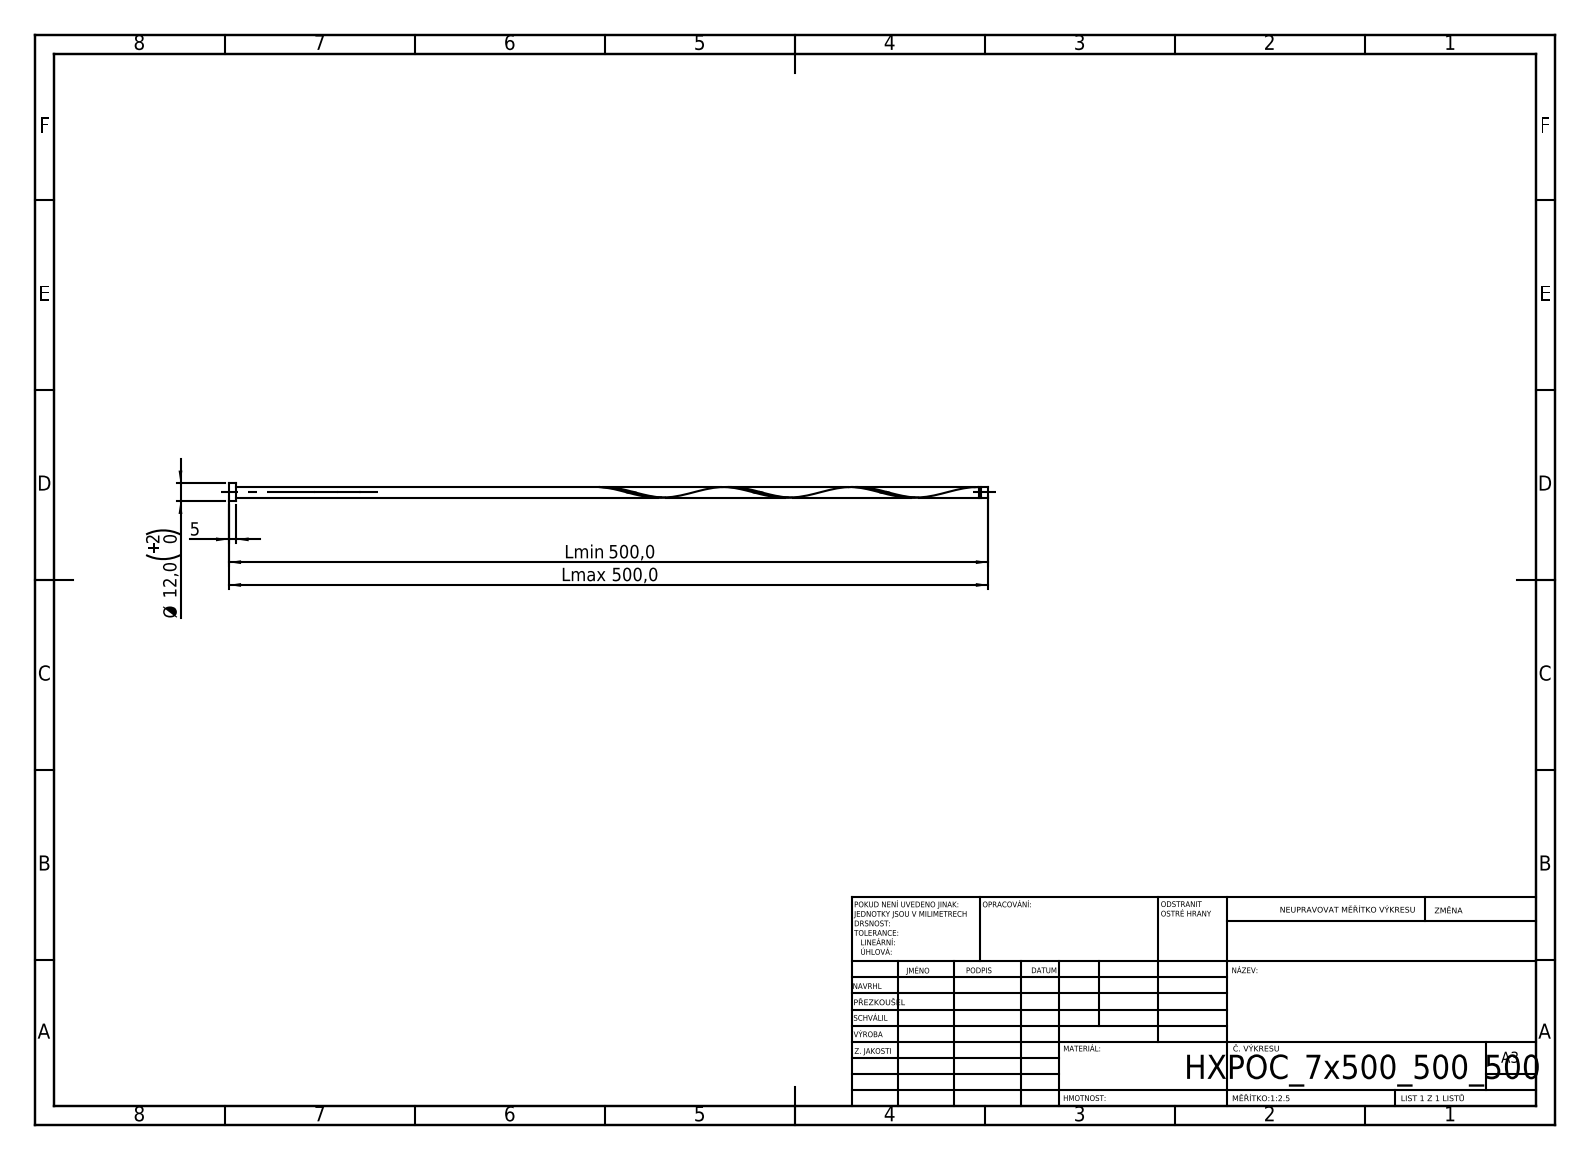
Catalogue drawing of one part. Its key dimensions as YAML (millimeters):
step_written_by: "SolidWorks 2019 (CONFIG_CONTROL_DESIGN)"
units: millimeters
bodies: {solids: 1, faces: 16, planar: 6, cylindrical: 9, other: 1}
overall_size: [500, 12, 12]
volume: 23687
surface_area: 15159
round_bosses_or_shafts:
  - {diameter: 12, count: 1}
  - {diameter: 7, count: 1}
  - {diameter: 5.6, count: 1}
face_to_face_distances: [5, 500, 495, 495.03, 490.03, 4.97, 493.63, 488.63, 1.4, 6.37]
